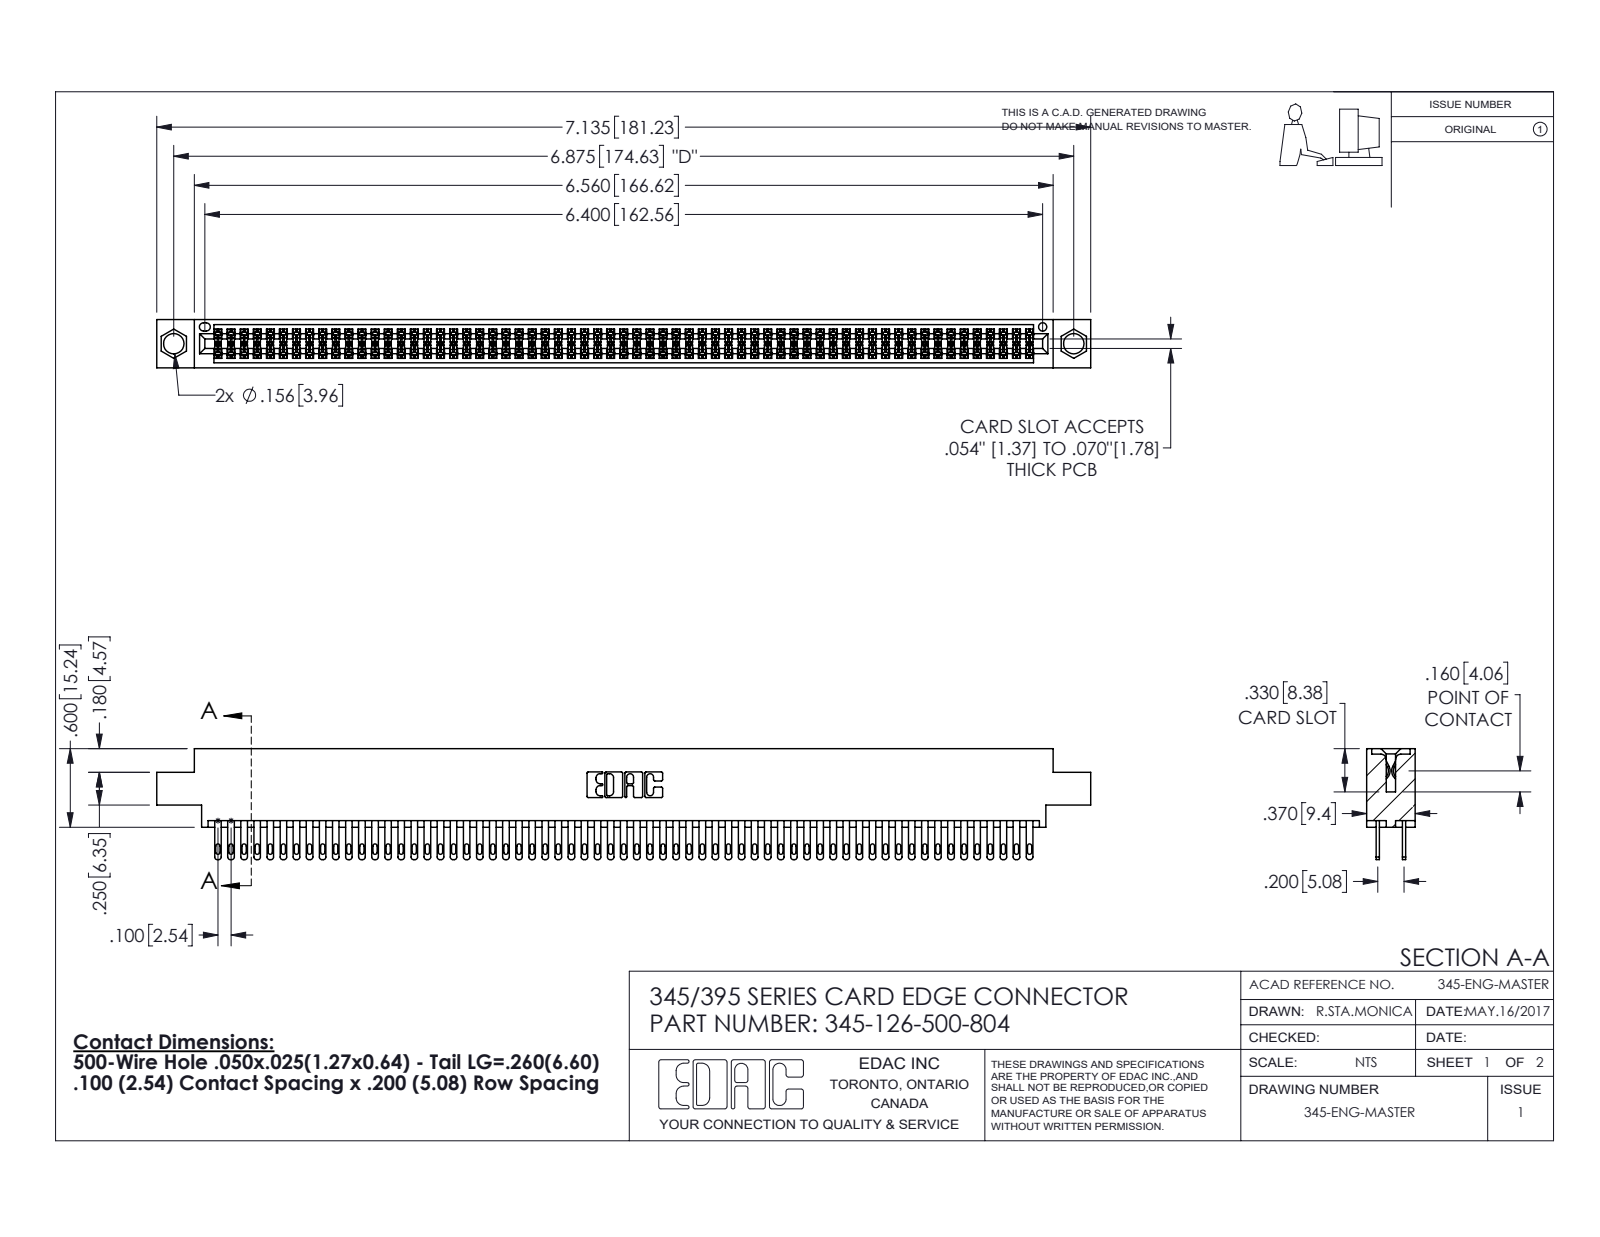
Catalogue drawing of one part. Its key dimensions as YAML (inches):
part_name: "345 Part_0.170 Offset - 0.156 Dia-TI; 345-126-500-804; 345-292-001_345-293-100"
step_written_by: "SolidWorks 2020 (CONFIG_CONTROL_DESIGN)"
units: inches
bodies: {solids: 127, faces: 5940, planar: 3500, cylindrical: 2440, other: 0}
overall_size: [7.135, 0.847, 0.37]
volume: 1.096
surface_area: 43.78
round_holes:
  - {diameter: 0.156, count: 2}
  - {diameter: 0.064, count: 1}
partial_cylinders:
  - {radius: 0.006, count: 189}
  - {radius: 0.016, count: 126}
  - {radius: 0.02, count: 126}
  - {radius: 0.01, count: 22}
  - {radius: 0.007, count: 6}
  - {radius: 0.031, count: 6}
  - {radius: 0.026, count: 3}
  - {radius: 0.014, count: 2}
face_to_face_distances: [0.072, 0.298, 0.2, 0.098, 0.272, 0.025, 0.37, 0.225, 0.175, 0.149]
hole_center_spacings: [0.27, 6.639, 6.875]
